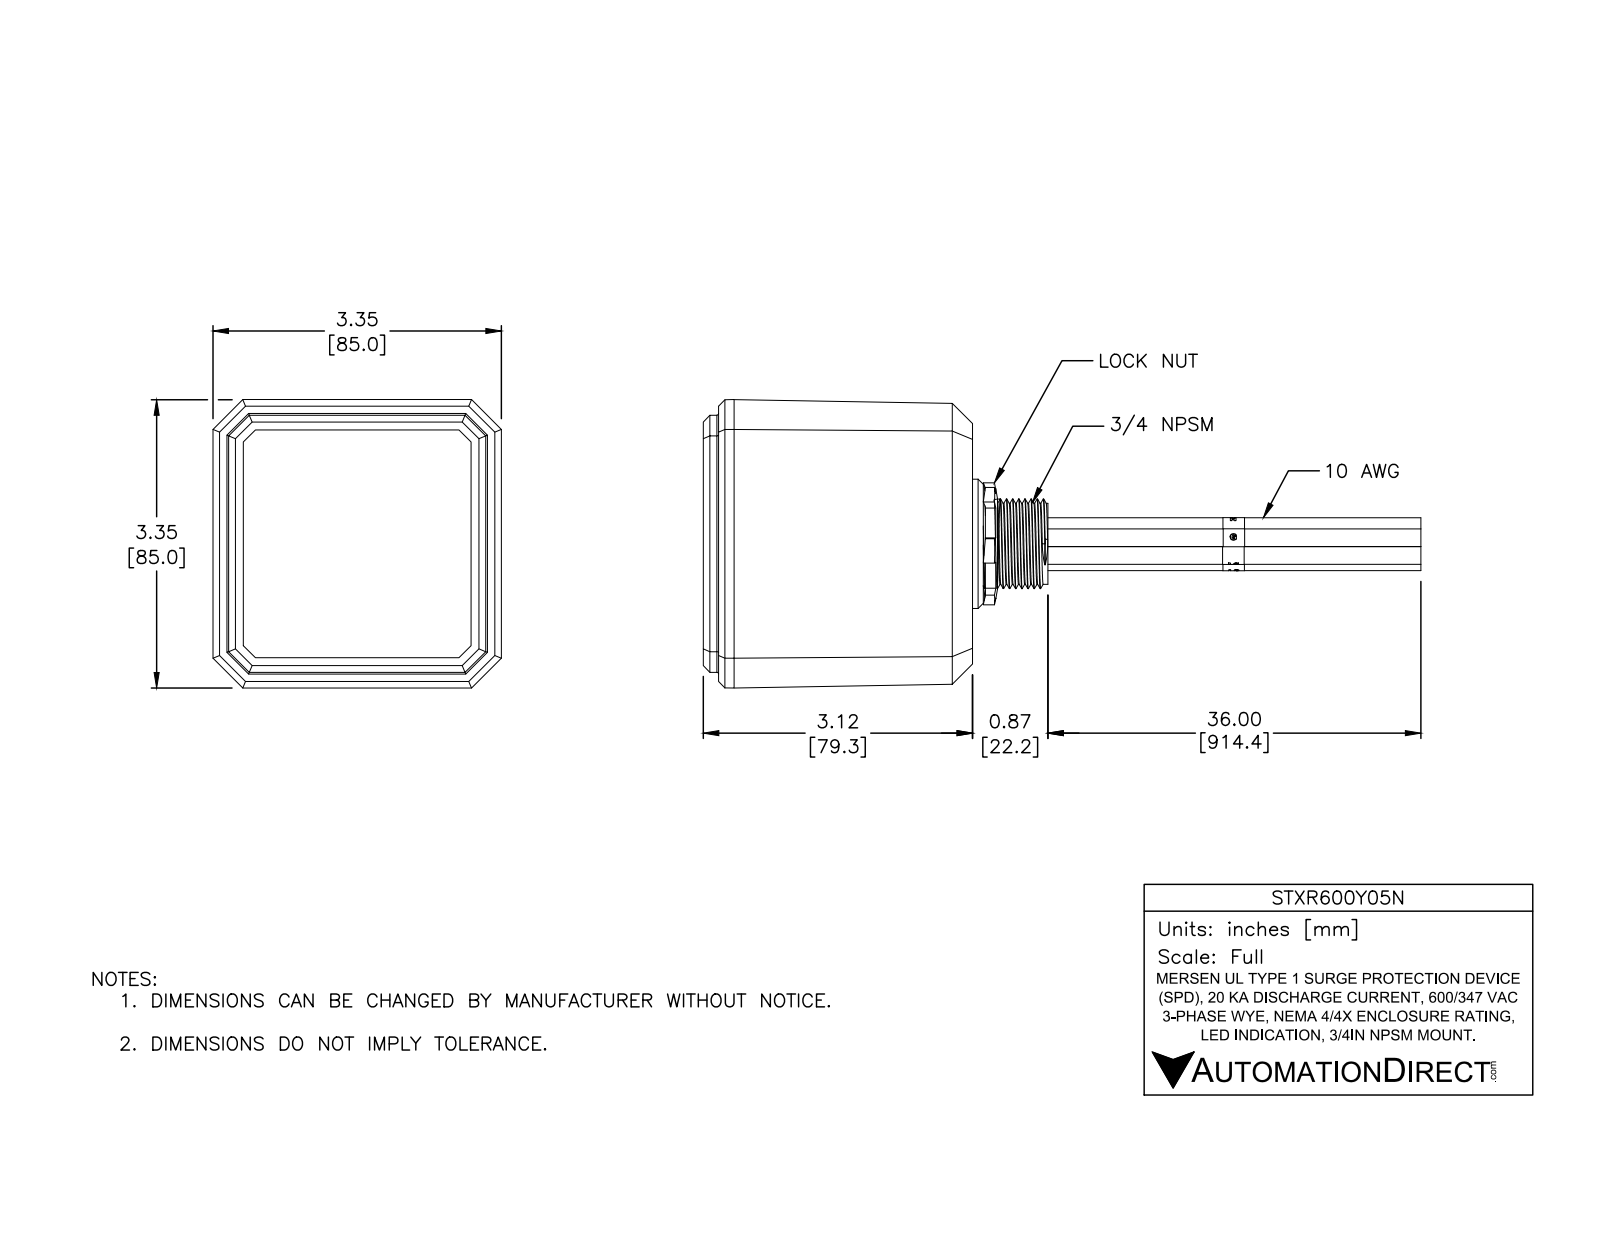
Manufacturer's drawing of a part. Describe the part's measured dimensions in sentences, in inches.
The part is named "STXR600Y05N". Its 3-D file was written by "SolidWorks 2016 (AUTOMOTIVE_DESIGN)". It is 8 solids with 525 faces: 318 planar, 123 cylindrical and 84 other. Overall it measures 8.327 by 3.347 by 3.347 inches. Its volume is 8.453 cubic inches and its surface area 148.8 square inches. Round holes: 1 of diameter 1. Round bosses or shafts: 15 of diameter 0.205, 3 of diameter 0.205, 3 of diameter 0.145, 2 of diameter 0.145, 1 of diameter 1.5, 1 of diameter 0.94. Partial cylindrical surfaces (rounded edges, fillets, slot ends): 16 of radius 0.015, 8 of radius 0.02, 8 of radius 0.1, 4 of radius 0.04, 1 of radius 0.31, 1 of radius 0.639. The main face-to-face distances are 0.125, 0.125, 0.12, 2.989, 3.109, 2.864, 2.984, 2.766, 2.641, 0.223.
